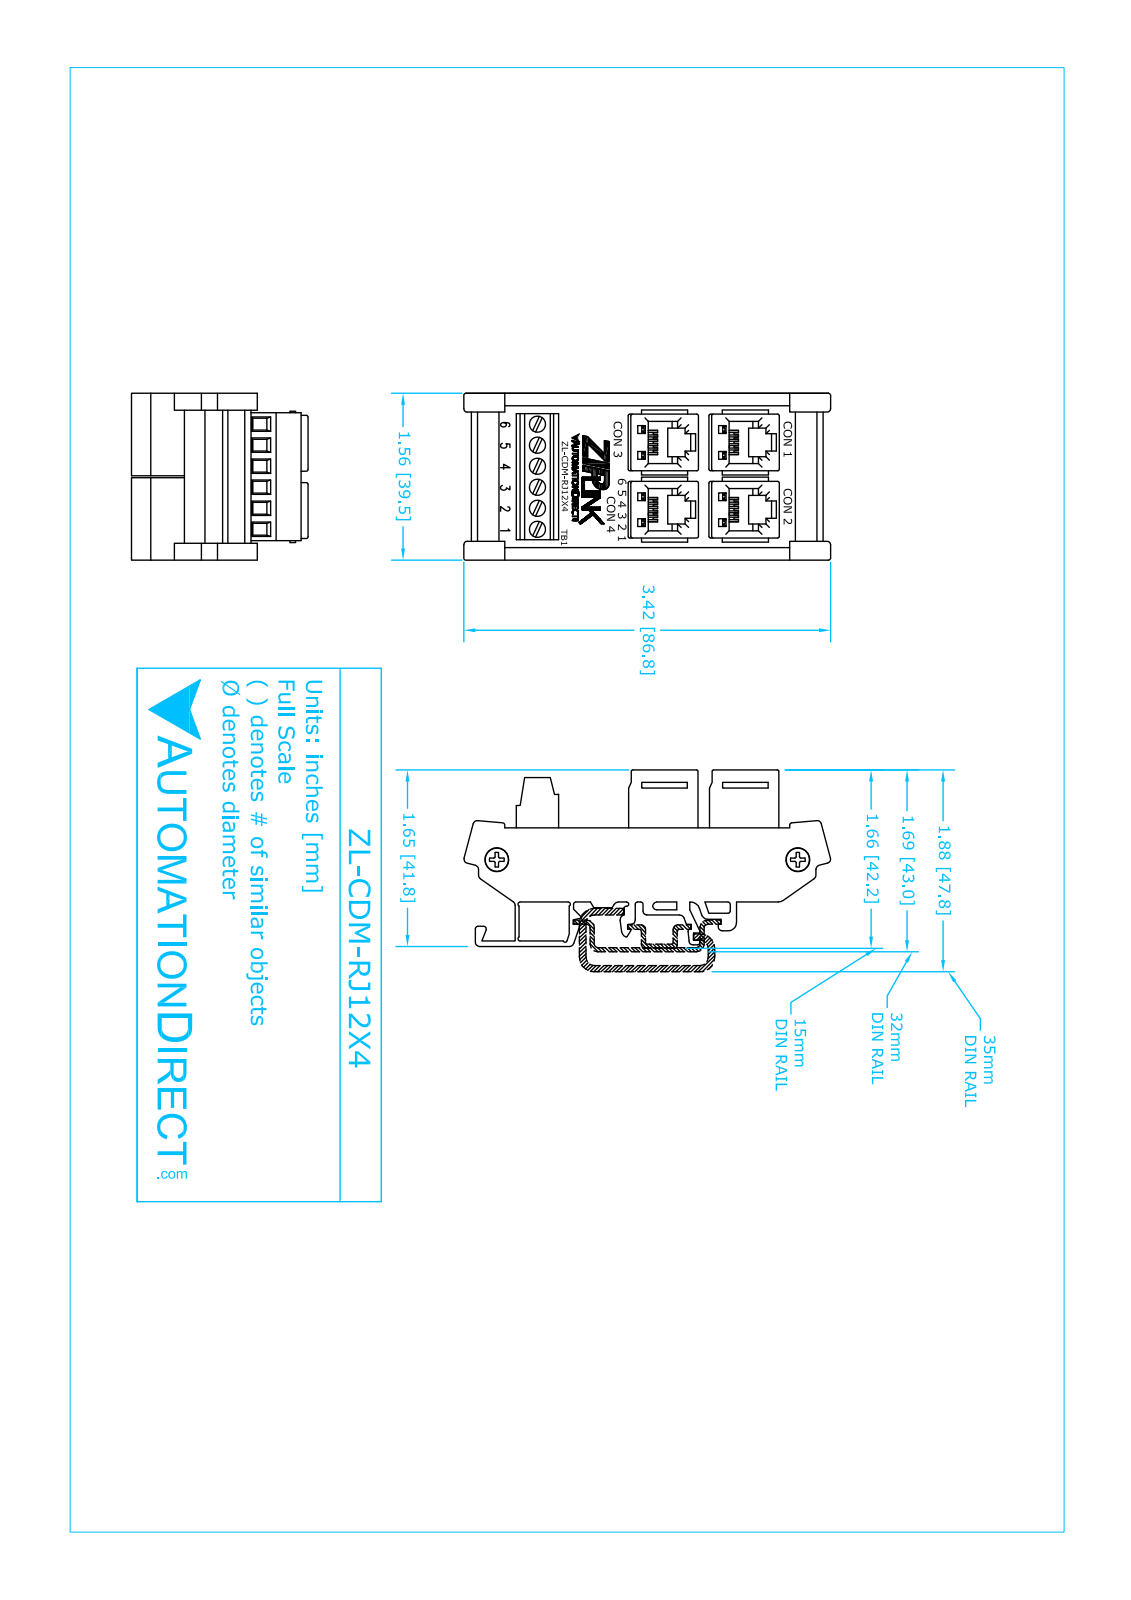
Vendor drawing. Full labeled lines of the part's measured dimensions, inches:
Part name (STEP PRODUCT): ZL-CDM-RJ12X4
STEP written by: SolidWorks 2014 (AUTOMOTIVE_DESIGN)
Units: inches
Bodies: 1 solid, 650 faces (481 planar, 161 cylindrical, 8 other)
Overall size (bounding box): 3.42 × 1.65 × 1.616
Volume: 4.205 in³ · Surface area: 41.87 in²
Round holes (diameter × count): ⌀0.15 ×6, ⌀0.225 ×2
Round bosses / shafts (diameter × count): ⌀0.205 ×2
Partial cylindrical surfaces — rounded edges, fillets, slot ends (radius × count): R0.03 ×42, R0.015 ×41
Main face-to-face distances: 1.56, 0.66, 0.75, 0.63, 1.08, 0.07, 0.03, 1.11, 0.034, 0.1
Hole centre spacings: 0.196, 0.392, 0.392, 0.588, 0.784, 0.196, 0.588, 0.98
